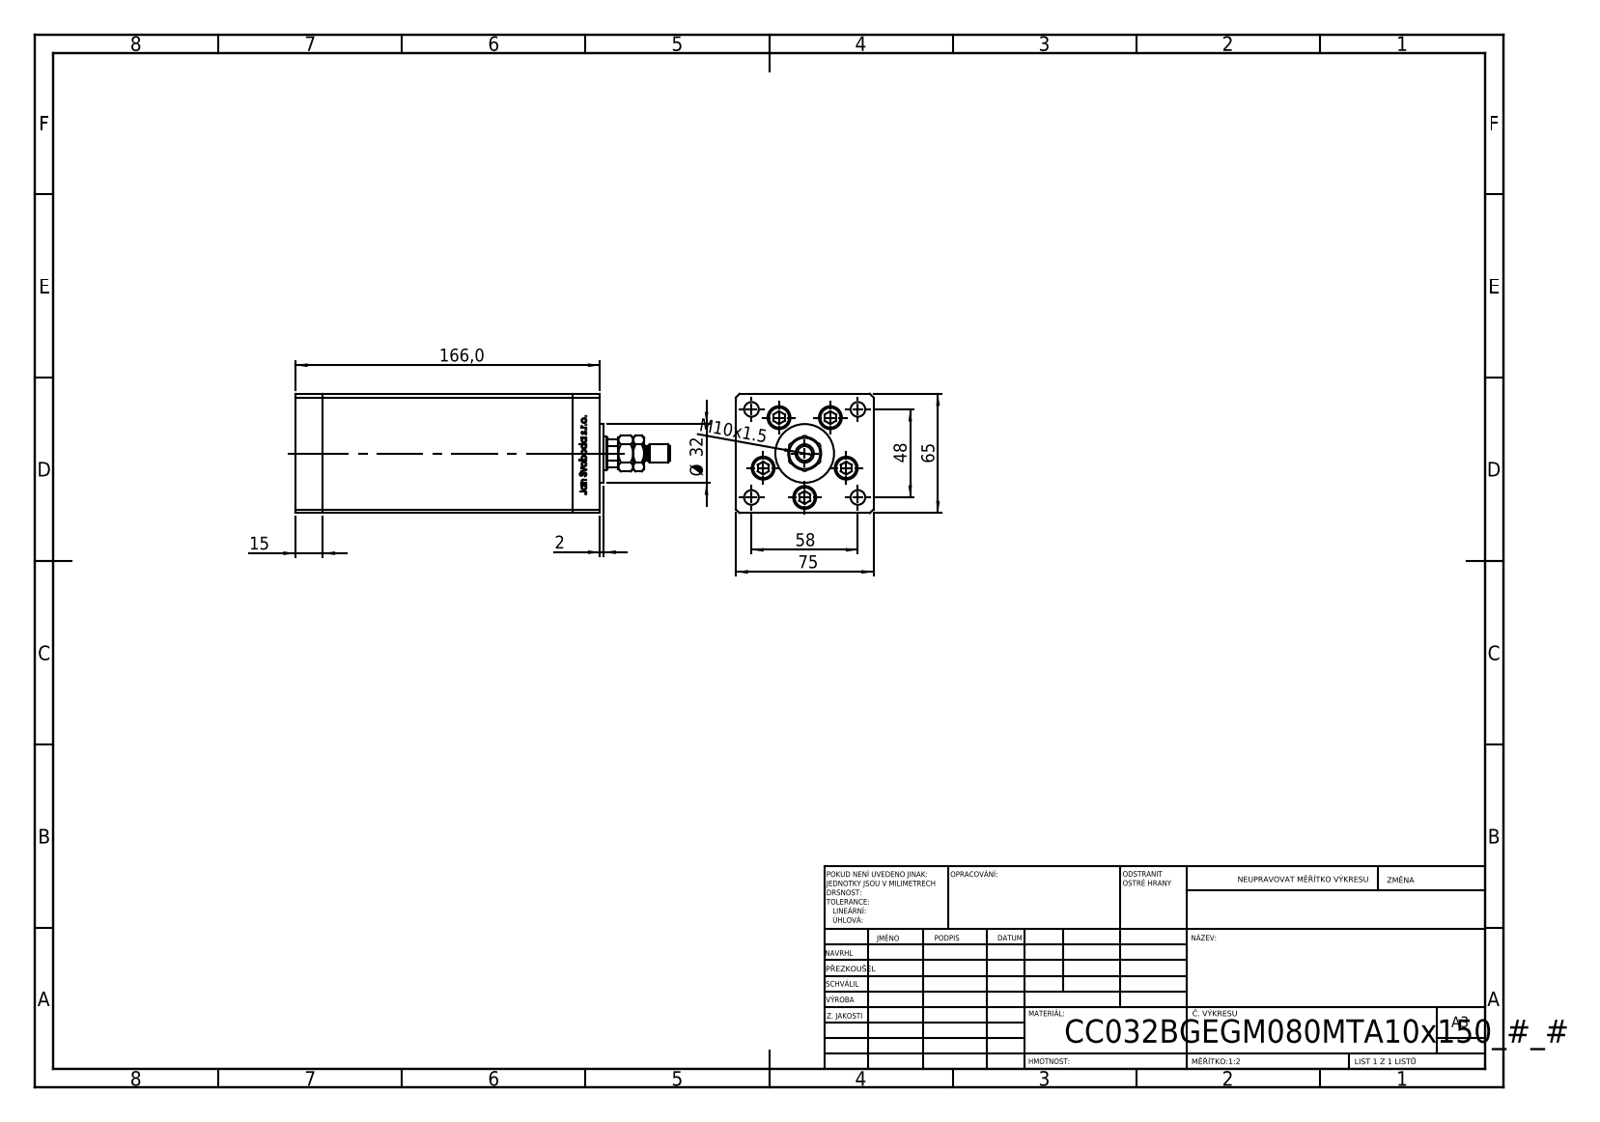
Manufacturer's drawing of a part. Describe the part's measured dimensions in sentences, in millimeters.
The part is named "ALLEN BOLT; V220C_FRONT_B; V220C_B MIDDLE; V220C_VC_B (+2 more)". Its 3-D file was written by "SolidWorks 2019 (CONFIG_CONTROL_DESIGN)". It is 15 solids with 1232 faces: 477 planar, 151 cylindrical and 604 other. Overall it measures 204 by 75 by 65 millimeters. Its volume is 726 984 cubic millimeters and its surface area 129 101 square millimeters. Round holes: 5 of diameter 9, 5 of diameter 12.5, 4 of diameter 8, 2 of diameter 2, 2 of diameter 13.16, 1 of diameter 8.5, 1 of diameter 18. Round bosses or shafts: 6 of diameter 8, 1 of diameter 32, 1 of diameter 10. Partial cylindrical surfaces (rounded edges, fillets, slot ends): 2 of radius 0.93, 1 of radius 8.5. The main face-to-face distances are 75, 65, 15, 136, 151, 166, 28, 13, 54.5, 10.5. The hole center spacings are 24, 37.64, 15.67, 17.22, 27.71, 28.83, 29, 32.63.
